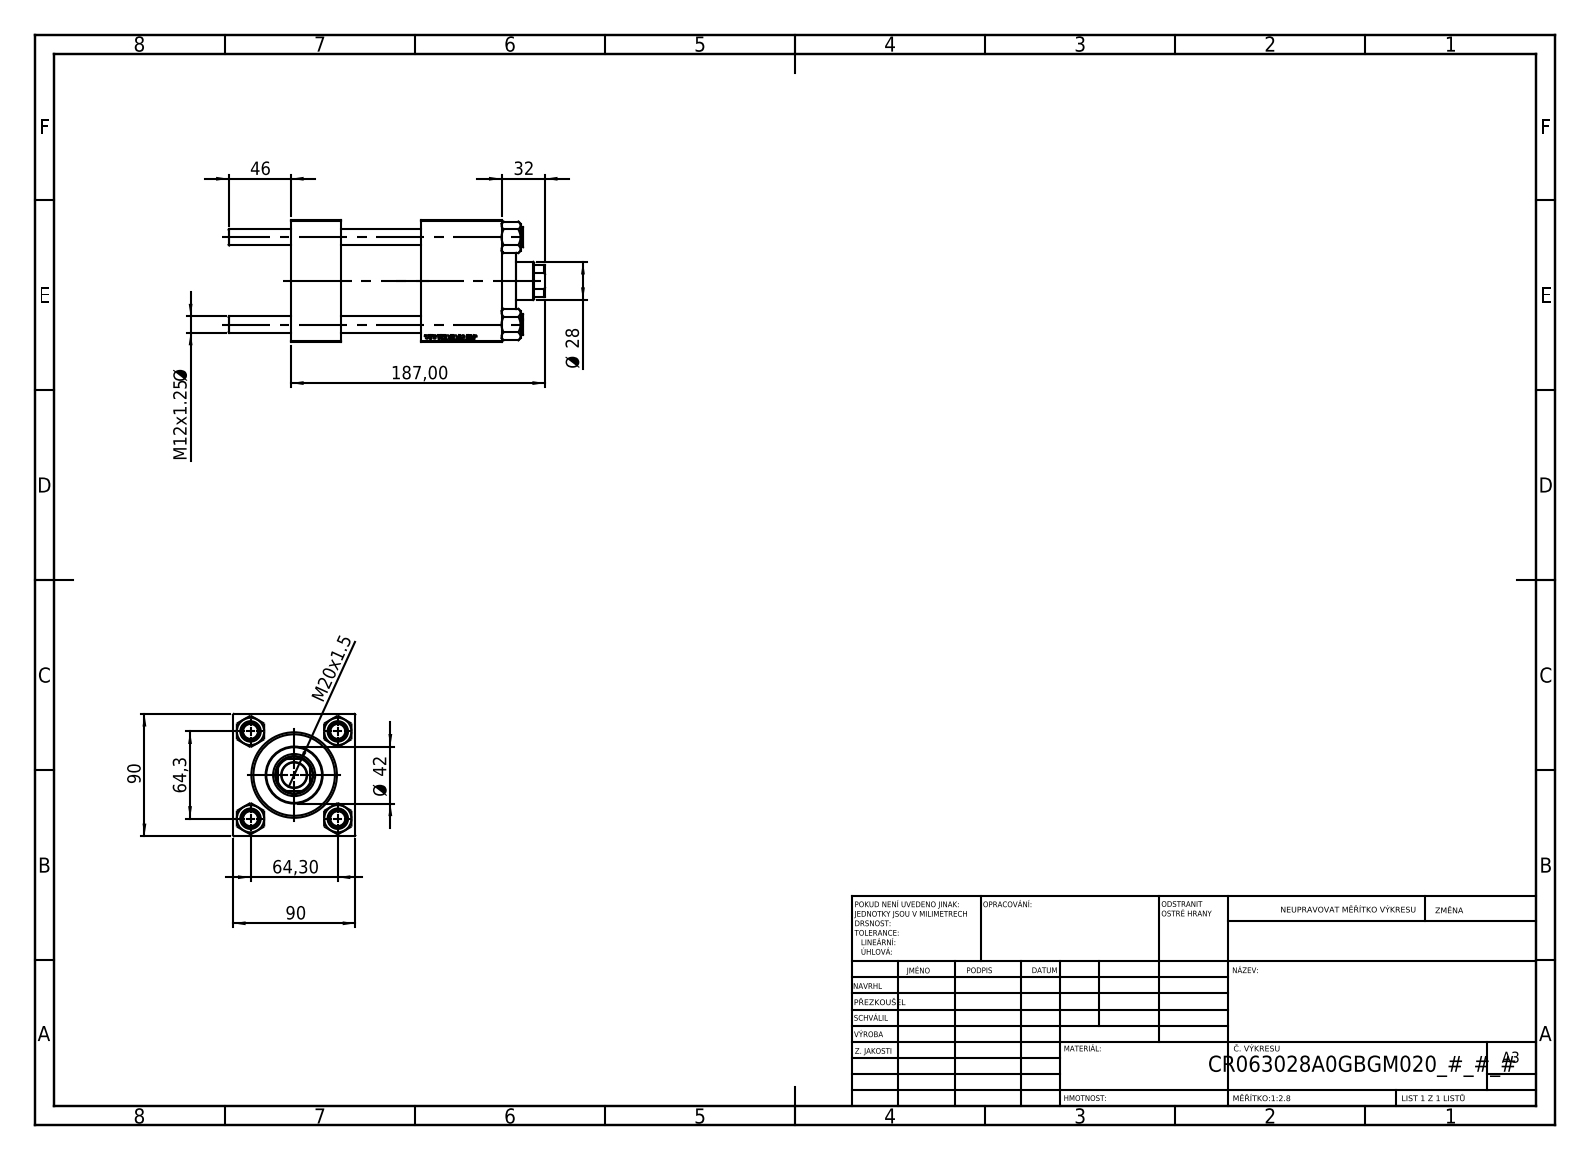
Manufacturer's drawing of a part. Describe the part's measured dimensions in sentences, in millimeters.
The part is named "V215_VC_A; CR025_012_A_0_G_A_G_M_020_+#_##_TYCINKA; NUT_M5; V215CR_VCP (+1 more)". Its 3-D file was written by "SolidWorks 2019 (CONFIG_CONTROL_DESIGN)". It is 11 solids with 1133 faces: 519 planar, 78 cylindrical and 536 other. Overall it measures 233 by 90 by 90 millimeters. Its volume is 980 811 cubic millimeters and its surface area 195 567 square millimeters. Round holes: 4 of diameter 12, 2 of diameter 7, 2 of diameter 20.96, 2 of diameter 30, 1 of diameter 18.5, 1 of diameter 28, 1 of diameter 31, 1 of diameter 50, 1 of diameter 60, 1 of diameter 63. Round bosses or shafts: 4 of diameter 15, 1 of diameter 69, 1 of diameter 42. Partial cylindrical surfaces (rounded edges, fillets, slot ends): 1 of radius 13.5. The main face-to-face distances are 90, 59, 37, 155, 118, 96, 126.3, 89.3, 30.3, 28.7. The hole center spacings are 45.47, 64.3, 90.93, 97.5.
